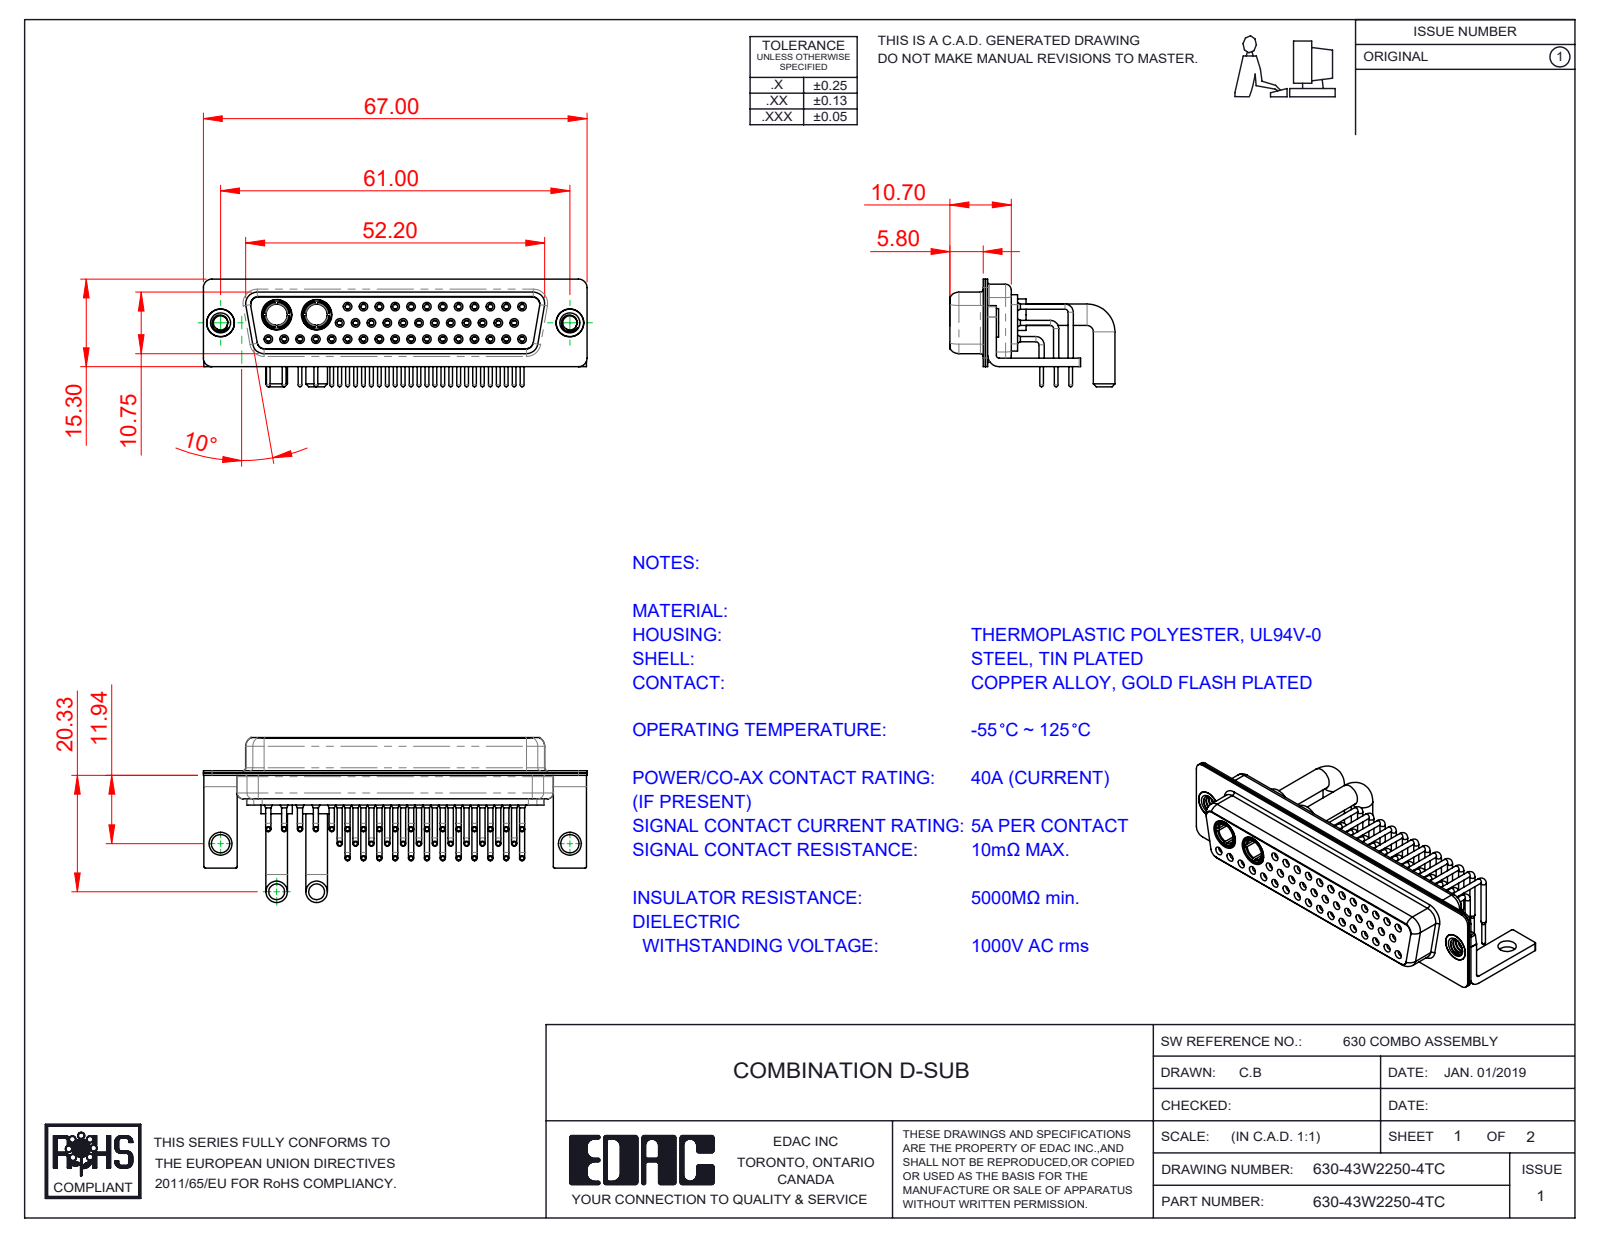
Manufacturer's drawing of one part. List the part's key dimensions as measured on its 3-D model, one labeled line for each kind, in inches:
Part name (STEP PRODUCT): 630-43W2250-4TC; 630Combo Contact Row 1_50 Contacts; 630Combo Stabilizer Bracket_50 Contacts; Power Socket_Ext 40A RA 50 (+6 more)
STEP written by: SolidWorks 2020 (CONFIG_CONTROL_DESIGN)
Units: inches
Bodies: 52 solids, 2646 faces (760 planar, 1148 cylindrical, 738 other)
Overall size (bounding box): 2.638 × 1.134 × 0.74
Volume: 0.482 in³ · Surface area: 26.1 in²
Round holes (diameter × count): ⌀0.035 ×41, ⌀0.043 ×41, ⌀0.059 ×41, ⌀0.079 ×41, ⌀0.063 ×29, ⌀0.067 ×12, ⌀0.191 ×4, ⌀0.098 ×2, ⌀0.126 ×2, ⌀0.146 ×2, ⌀0.157 ×2, ⌀0.159 ×2
Round bosses / shafts (diameter × count): ⌀0.035 ×41, ⌀0.026 ×41, ⌀0.063 ×12, ⌀0.148 ×4, ⌀0.217 ×2, ⌀0.205 ×2, ⌀0.197 ×2, ⌀0.195 ×2
Partial cylindrical surfaces — rounded edges, fillets, slot ends (radius × count): R0.01 ×16, R0.059 ×16, R0.079 ×13, R0.053 ×12, R0.063 ×8, R0.02 ×5, R0.024 ×4, R0.026 ×4
Main face-to-face distances: 0.016, 0.059, 0.236, 0.22, 0.031, 0.228, 0.205, 0.444, 0.072, 0.407
Hole centre spacings: 0.109, 0.124, 0.218, 0.327, 0.436, 0.545, 0.654, 0.763
